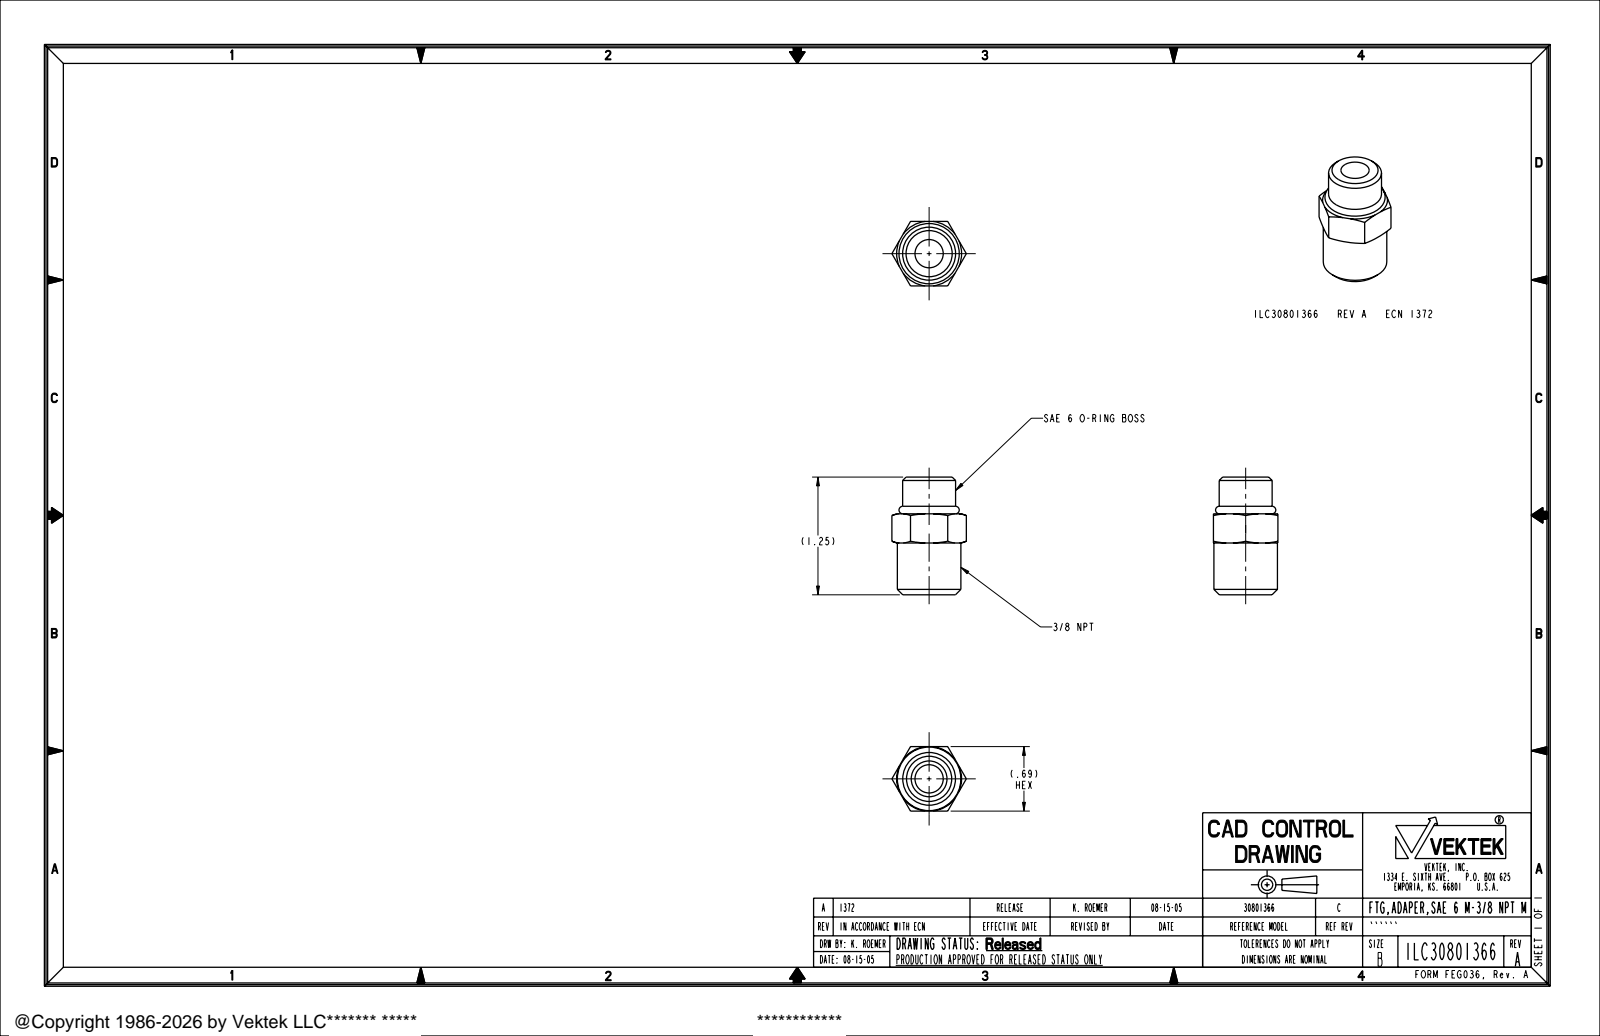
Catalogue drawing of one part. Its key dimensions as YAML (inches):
part_name: "ILC30801366"
step_written_by: "PRO/ENGINEER BY PARAMETRIC TECHNOLOGY CORPORATION, 2004290 (AUTOMOTIVE_DESIGN_CC2)"
units: inches
bodies: {solids: 1, faces: 39, planar: 11, cylindrical: 8, other: 20}
overall_size: [1.25, 0.791, 0.685]
volume: 0.299
surface_area: 4.535
round_holes:
  - {diameter: 0.3, count: 1}
  - {diameter: 0.38, count: 1}
round_bosses_or_shafts:
  - {diameter: 0.675, count: 1}
  - {diameter: 0.563, count: 1}
face_to_face_distances: [0.685, 0.39, 0.86, 1.25, 0.69, 0.17, 0.56, 0.55, 0.14, 0.31]
